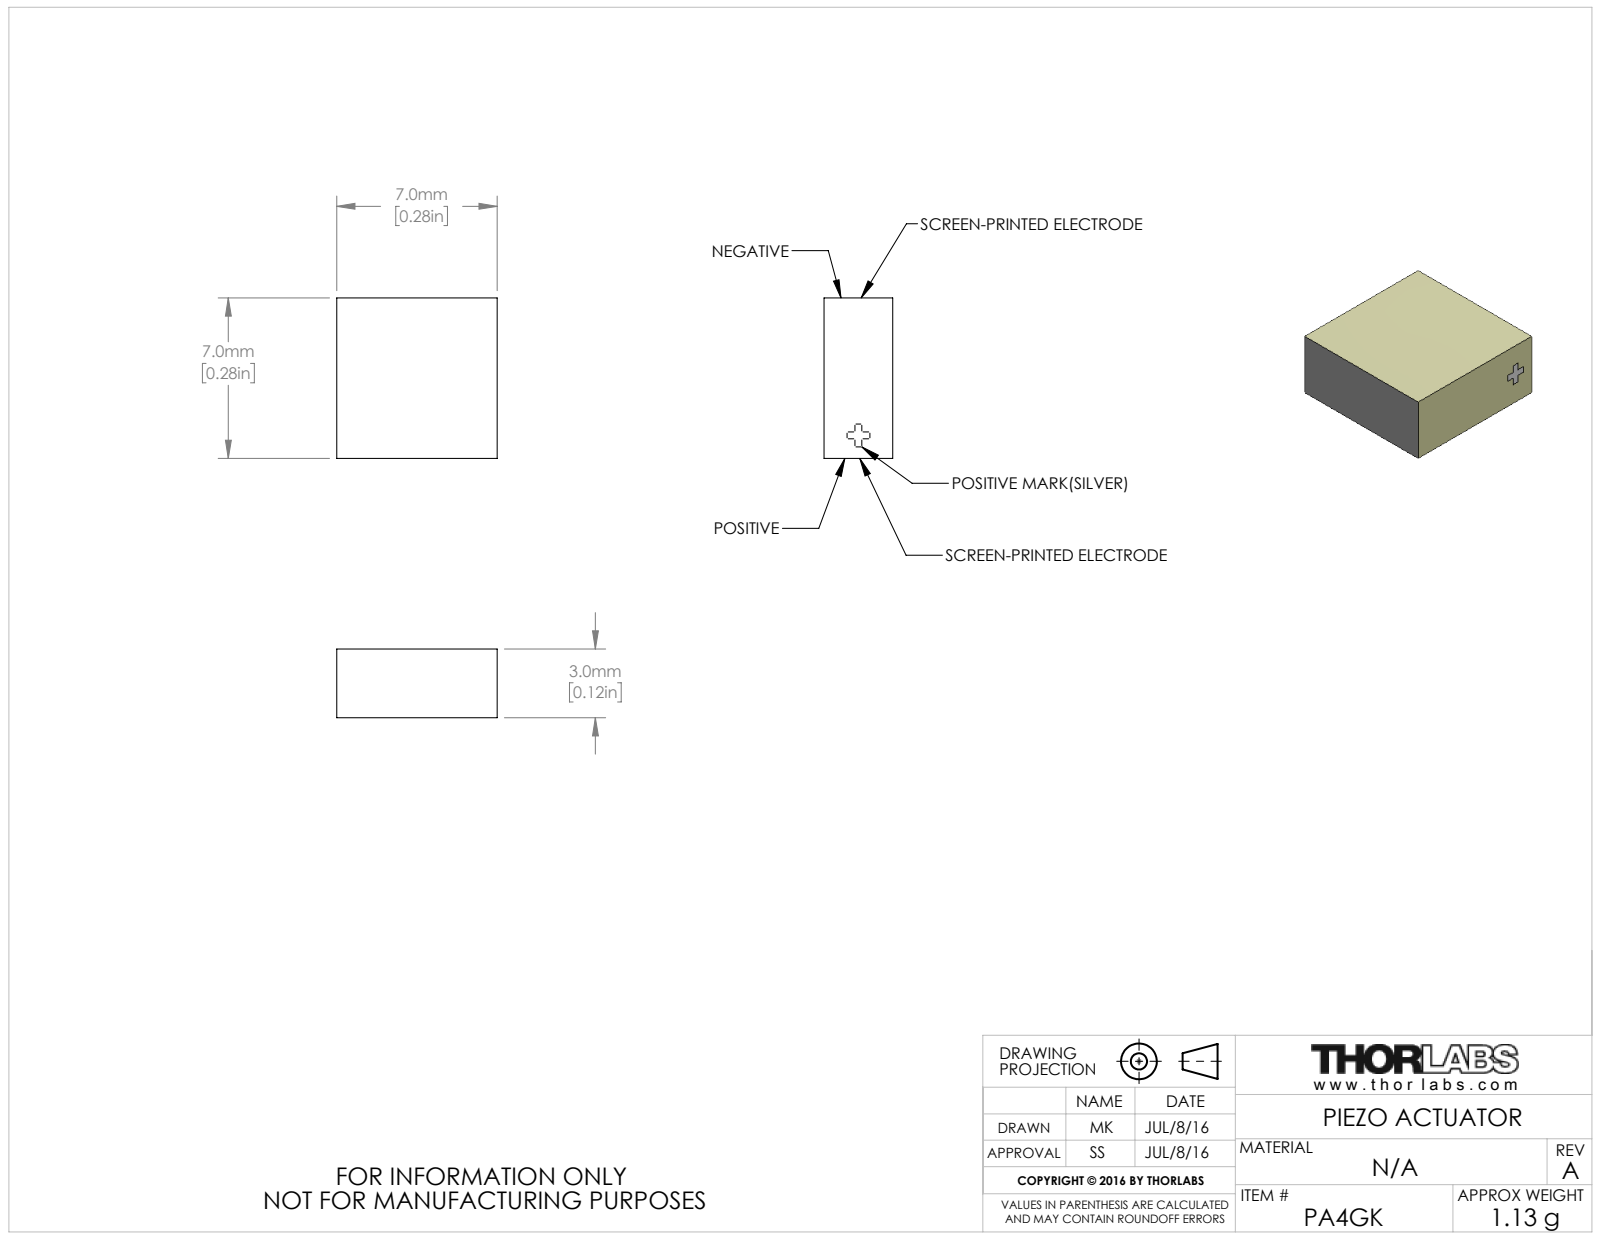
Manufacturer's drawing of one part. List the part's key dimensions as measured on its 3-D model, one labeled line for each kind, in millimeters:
Part name (STEP PRODUCT): CTN003168
STEP written by: SolidWorks 2016 (AUTOMOTIVE_DESIGN)
Units: millimetres
Bodies: 1 solid, 7 faces (7 planar, 0 cylindrical, 0 other)
Overall size (bounding box): 7 × 7 × 3
Volume: 147 mm³ · Surface area: 182 mm²
Main face-to-face distances: 3, 7
